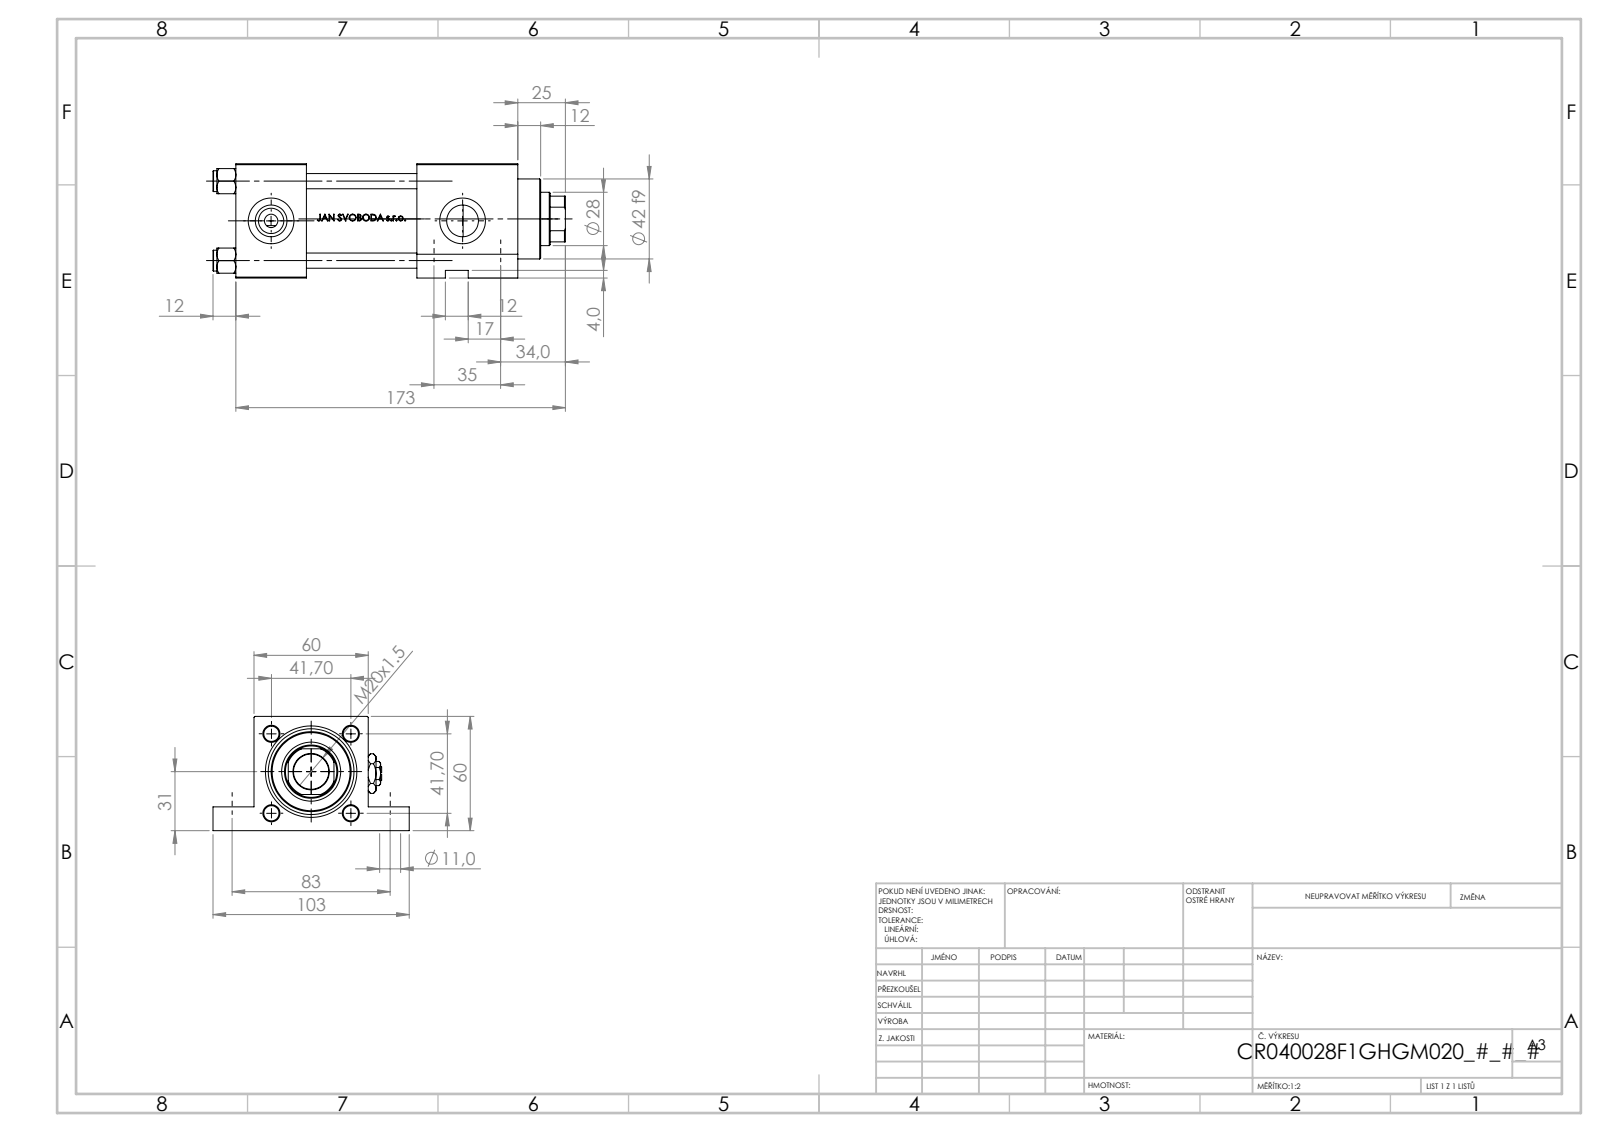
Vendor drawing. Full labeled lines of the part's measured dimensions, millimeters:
Part name (STEP PRODUCT): V215CR_F_Body; NUT_M5_F; V215CR_VCP_F; V215CR_F_TYCINKA (+2 more)
STEP written by: SolidWorks 2019 (CONFIG_CONTROL_DESIGN)
Units: millimetres
Bodies: 12 solids, 1166 faces (461 planar, 145 cylindrical, 560 other)
Overall size (bounding box): 185 × 103 × 60
Volume: 443 348 mm³ · Surface area: 118 907 mm²
Round holes (diameter × count): ⌀8 ×4, ⌀16.66 ×3, ⌀24 ×3, ⌀7 ×2, ⌀11 ×2, ⌀11 ×2, ⌀18.5 ×1, ⌀28 ×1, ⌀31 ×1, ⌀40 ×1, ⌀45 ×1
Round bosses / shafts (diameter × count): ⌀11 ×4, ⌀46 ×1, ⌀42 ×1
Partial cylindrical surfaces — rounded edges, fillets, slot ends (radius × count): R13.5 ×1
Main face-to-face distances: 60, 37, 58, 95, 148, 53, 111, 12.5, 47.5, 38
Hole centre spacings: 41.7, 28.79, 30.2, 35, 58.97, 83, 90.08, 8
